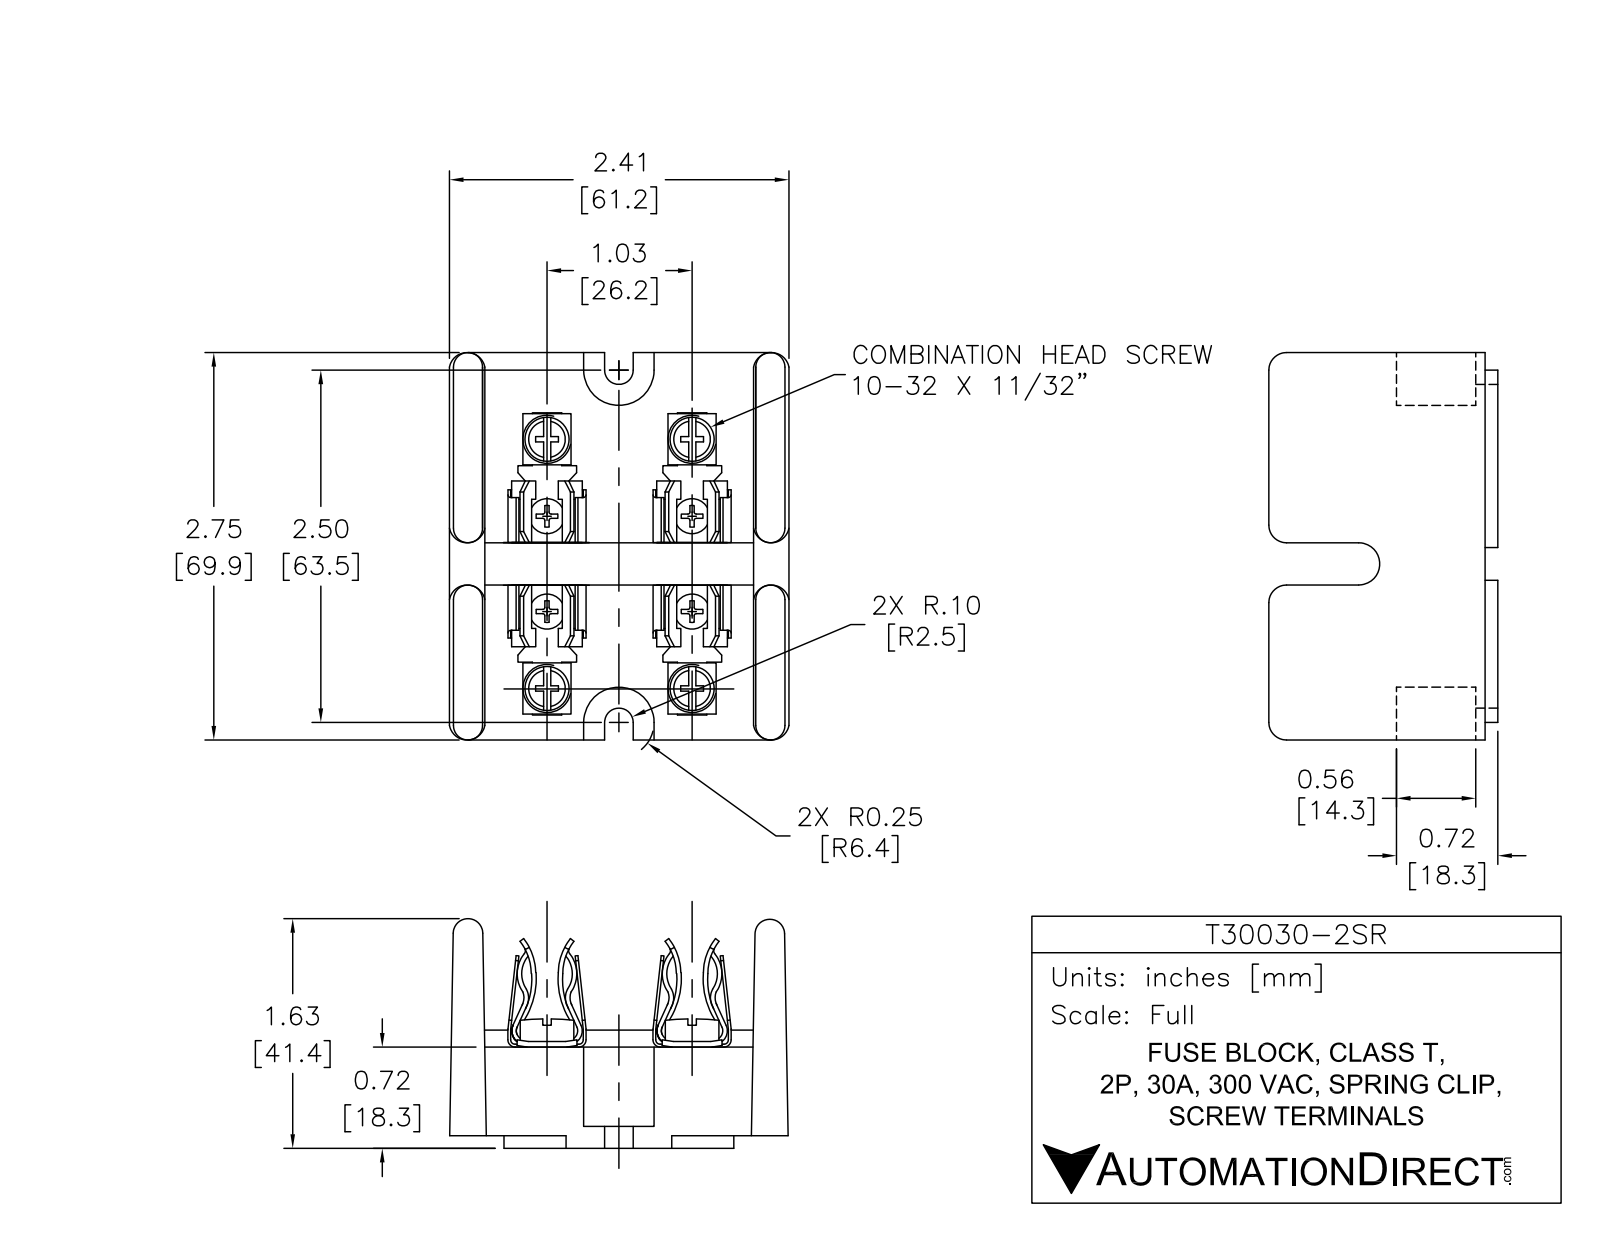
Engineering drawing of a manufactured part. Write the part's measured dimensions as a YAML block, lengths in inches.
part_name: "T30030-2SR"
step_written_by: "SolidWorks 2019 (AUTOMOTIVE_DESIGN)"
units: inches
bodies: {solids: 9, faces: 403, planar: 204, cylindrical: 167, other: 32}
overall_size: [2.75, 2.409, 1.63]
volume: 5.771
surface_area: 42.46
round_bosses_or_shafts:
  - {diameter: 0.375, count: 4}
partial_cylinders:
  - {radius: 0.2, count: 16}
  - {radius: 0.125, count: 15}
  - {radius: 0.24, count: 8}
  - {radius: 0.184, count: 4}
  - {radius: 0.224, count: 4}
  - {radius: 0.235, count: 4}
  - {radius: 0.1, count: 2}
  - {radius: 0.172, count: 2}
face_to_face_distances: [0.68, 2.409, 0.25, 2.159, 0.74, 0.06, 0.78, 0.72, 0.04, 1.909]
